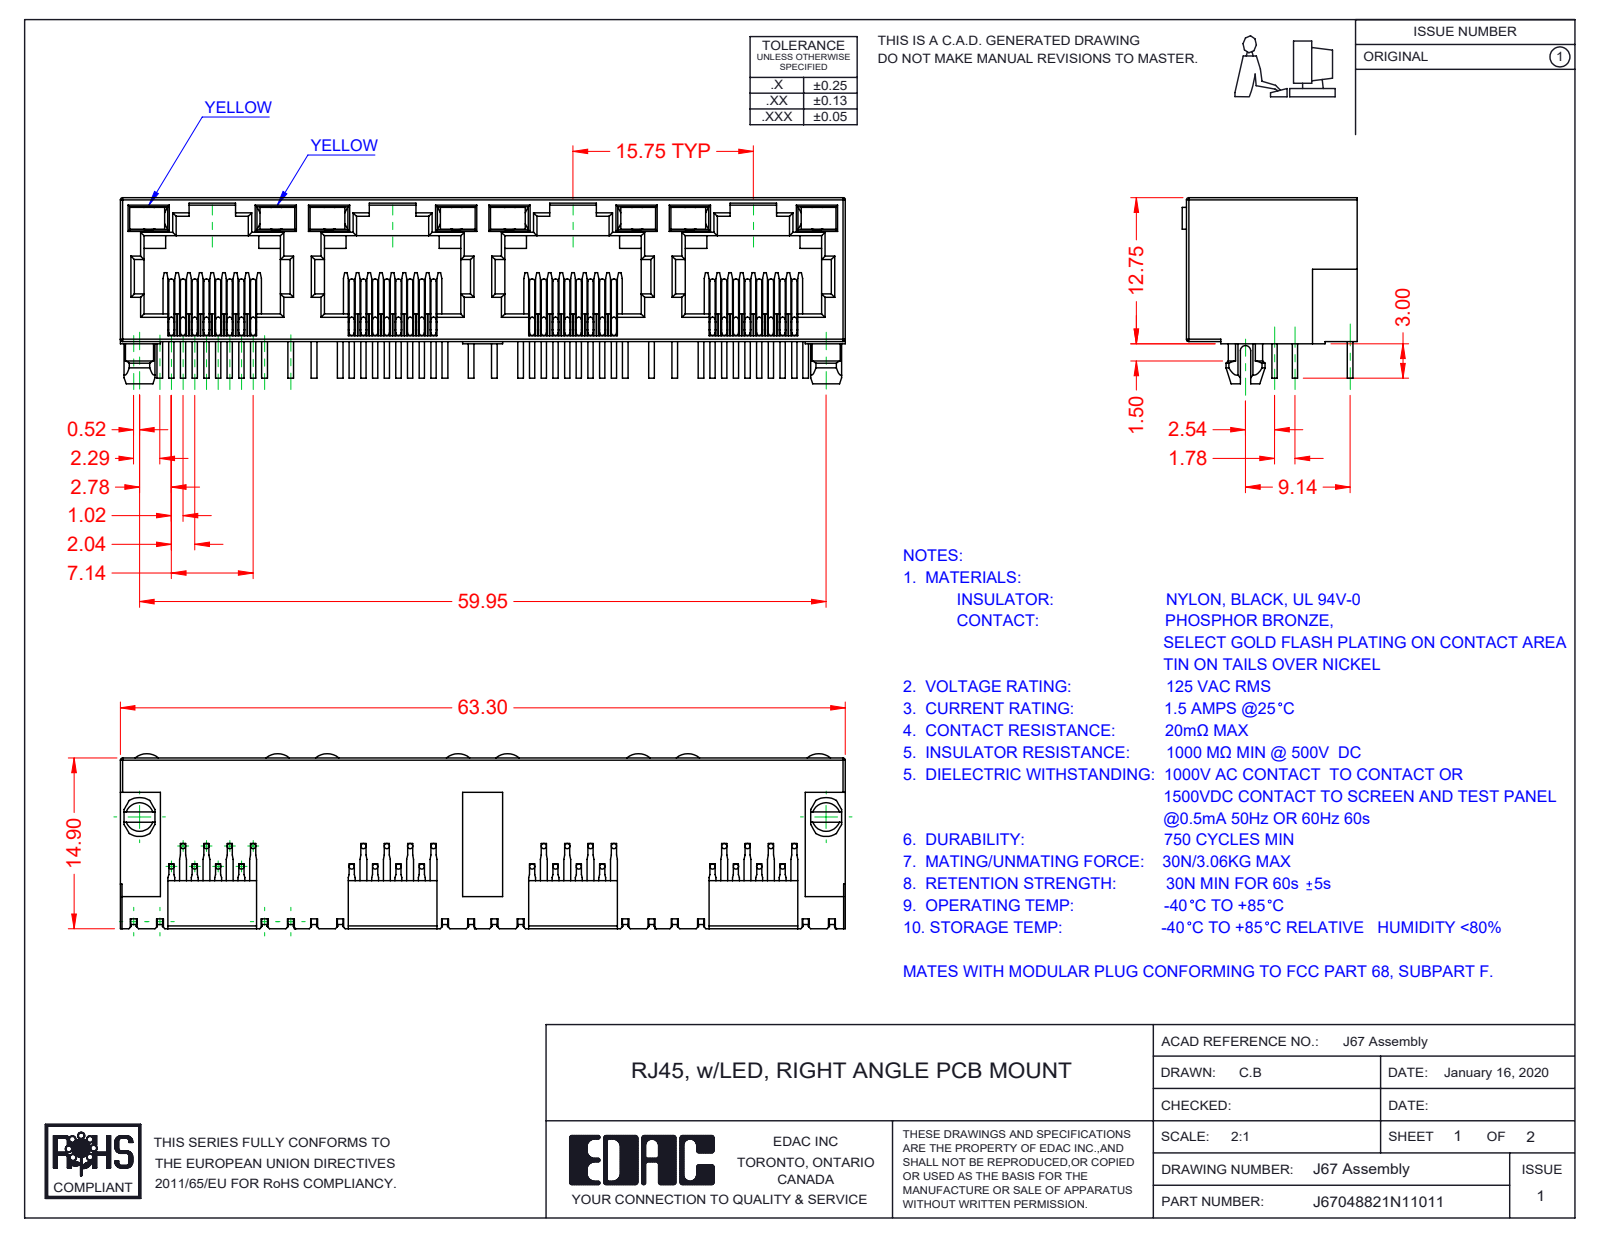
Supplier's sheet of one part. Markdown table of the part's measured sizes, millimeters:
| quantity | value |
| --- | --- |
| part name | 67 Contacts; 67 LED RH_1-Yellow; 67 Insulator; J67048822N11011 (+1 more) |
| STEP written by | SolidWorks 2016 (CONFIG_CONTROL_DESIGN) |
| units | millimeters |
| bodies | 41 solids, 2465 faces (1781 planar, 476 cylindrical, 208 other) |
| overall size | 63.3 × 16.25 × 15.28 |
| volume | 5 159 mm³ |
| surface area | 11 573 mm² |
| round bosses / shafts (diameter × count) | 0.46 × 96 |
| partial cylindrical surfaces (radius × count) | 0.2 × 66, 0.3 × 29, 0.45 × 9, 1.55 × 8, 1.5 × 2, 1.7 × 2, 0.35 × 1, 1 × 1 |
| main face-to-face distances | 0.5, 12.55, 1.89, 0.89, 10, 15.75, 1, 1.39, 11, 11.89 |
